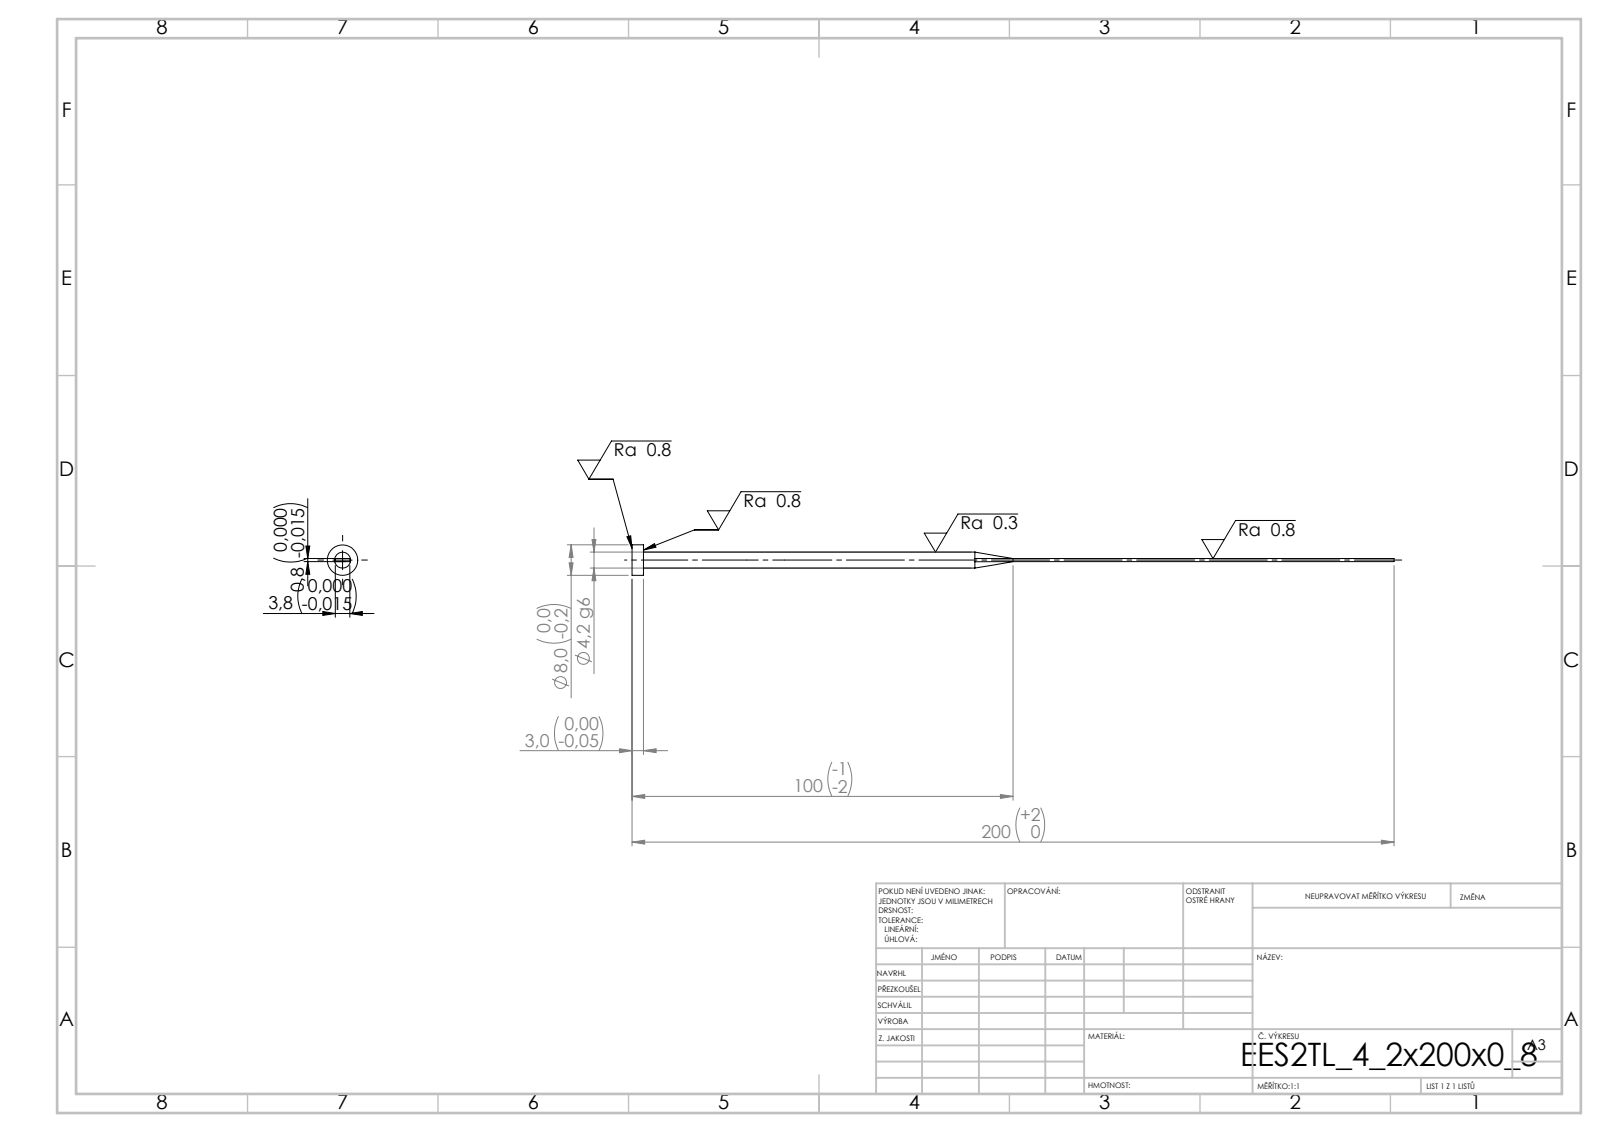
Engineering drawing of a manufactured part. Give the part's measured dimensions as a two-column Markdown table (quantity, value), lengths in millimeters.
| quantity | value |
| --- | --- |
| STEP written by | SolidWorks 2019 (CONFIG_CONTROL_DESIGN) |
| units | millimeters |
| bodies | 1 solid, 15 faces (7 planar, 4 cylindrical, 4 other) |
| overall size | 200 × 8 × 8 |
| volume | 1 740 mm³ |
| surface area | 2 341 mm² |
| round bosses / shafts (diameter × count) | 8 × 1, 4.2 × 1 |
| main face-to-face distances | 0.8, 3.8, 3, 200, 197 |
